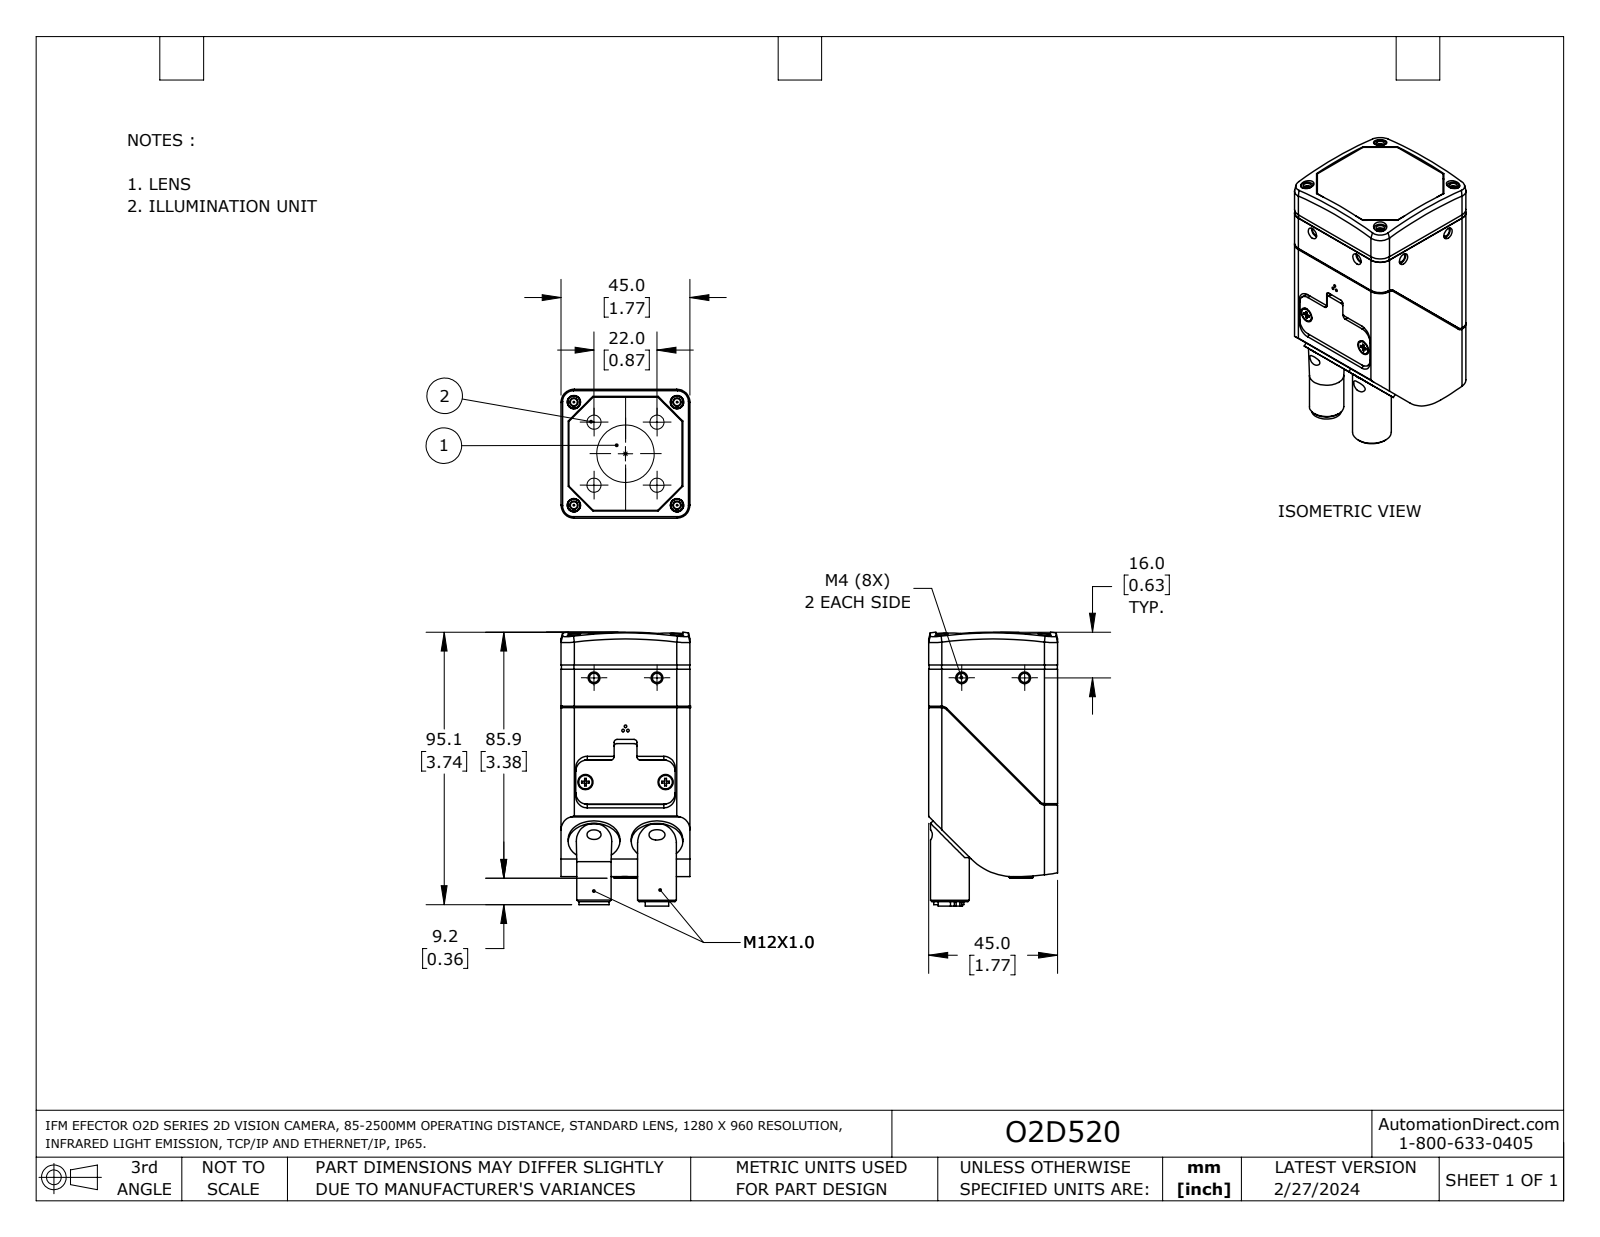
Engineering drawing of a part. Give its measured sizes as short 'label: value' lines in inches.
name: O2D5xx
written by: SolidWorks 2023 (AUTOMOTIVE_DESIGN)
unit: in
bodies: 1 solid, 302 faces (159 planar, 101 cylindrical, 42 other)
size: 3.765 × 1.772 × 1.772
volume: 10 in³; area: 35.29 in²
holes: 4× ⌀0.098, 4× ⌀0.115, 4× ⌀0.122, 4× ⌀0.128, 4× ⌀0.161, 3× ⌀0.035, 1× ⌀0.327, 1× ⌀0.43
bosses: 4× ⌀0.173, 4× ⌀0.169, 2× ⌀0.708, 2× ⌀0.185, 1× ⌀0.531, 1× ⌀0.472, 1× ⌀0.421, 1× ⌀0.413
rounds: 4× R0.039, 4× R0.098, 4× R0.157, 4× R0.169, 4× R0.174, 4× R0.181, 2× R0.043, 1× R0.02
face distances: 1.772, 1.768, 1.673, 0.098, 1.669, 0.094, 0.108, 1.663, 0.104, 1.659
hole spacings: 0.067, 0.866, 0.794, 0.827, 0.861, 1.417, 1.418, 2.005
